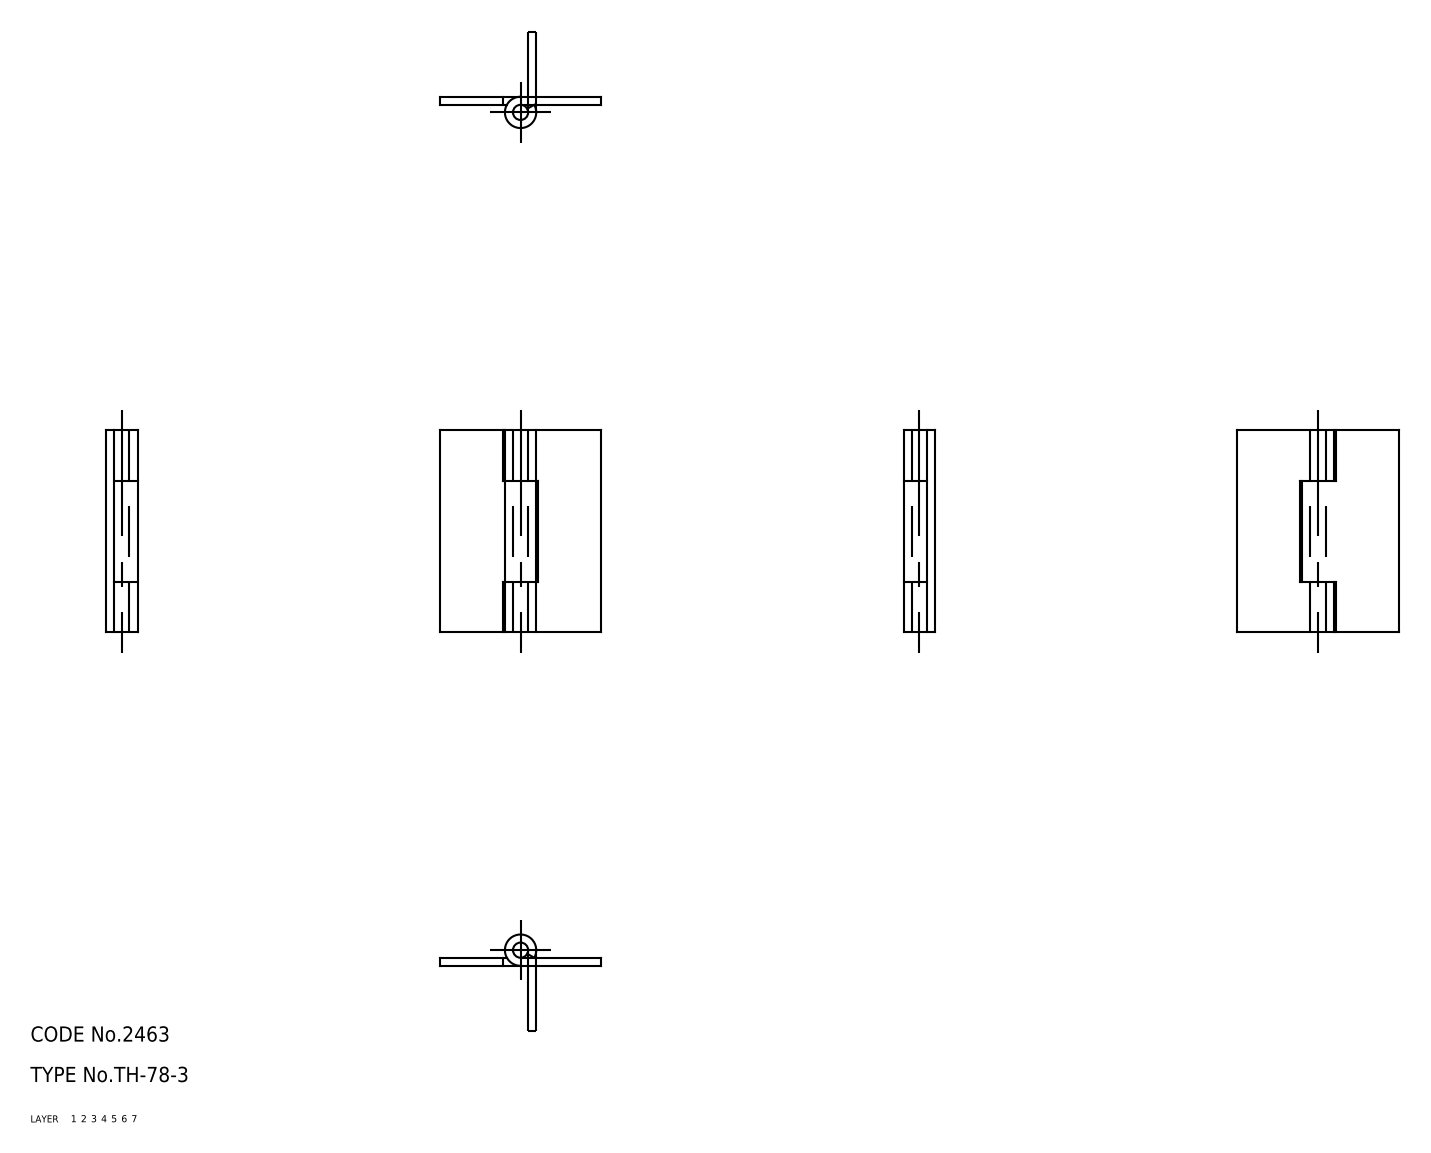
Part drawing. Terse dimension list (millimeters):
name: hinge piece_B; hinge piece_A; shaft; TH_78_3_16671_36
written by: CADfix (AUTOMOTIVE_DESIGN)
unit: mm
bodies: 3 solids, 30 faces (0 planar, 0 cylindrical, 30 other)
size: 40 × 32 × 6.2
volume: 2 873 mm³; area: 4 113 mm²
